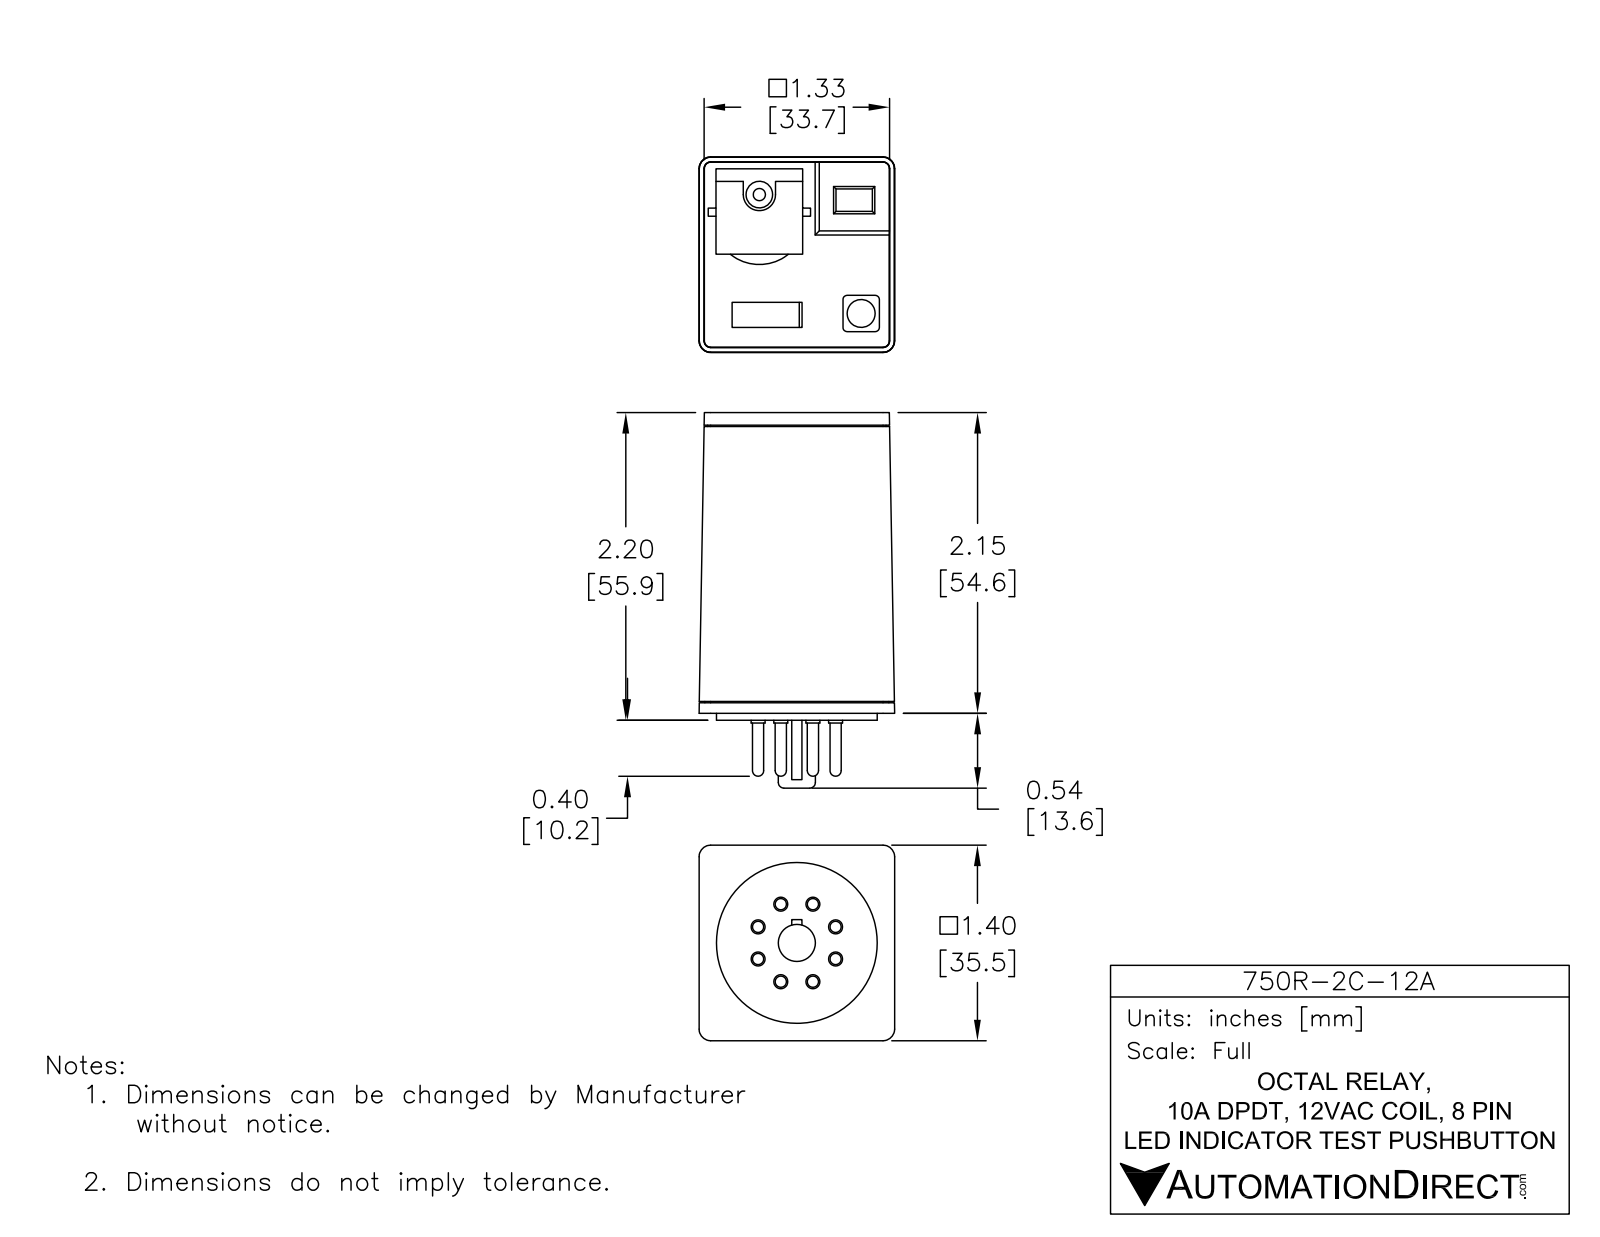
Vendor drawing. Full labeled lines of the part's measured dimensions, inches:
Part name (STEP PRODUCT): 750R-2C-24D
STEP written by: SolidWorks 2014 (AUTOMOTIVE_DESIGN)
Units: inches
Bodies: 1 solid, 162 faces (90 planar, 50 cylindrical, 22 other)
Overall size (bounding box): 2.685 × 1.398 × 1.398
Volume: 4.047 in³ · Surface area: 17.37 in²
Round holes (diameter × count): ⌀0.087 ×1, ⌀0.2 ×1
Round bosses / shafts (diameter × count): ⌀0.1 ×8, ⌀0.08 ×8, ⌀1.15 ×1, ⌀0.265 ×1, ⌀0.19 ×1
Partial cylindrical surfaces — rounded edges, fillets, slot ends (radius × count): R0.03 ×4, R0.115 ×1, R0.33 ×1
Main face-to-face distances: 0.05, 2.15, 2.2, 2.11, 0.04, 2.19, 2.14, 0.085, 0.03, 2.16
Hole centre spacings: 1.119
